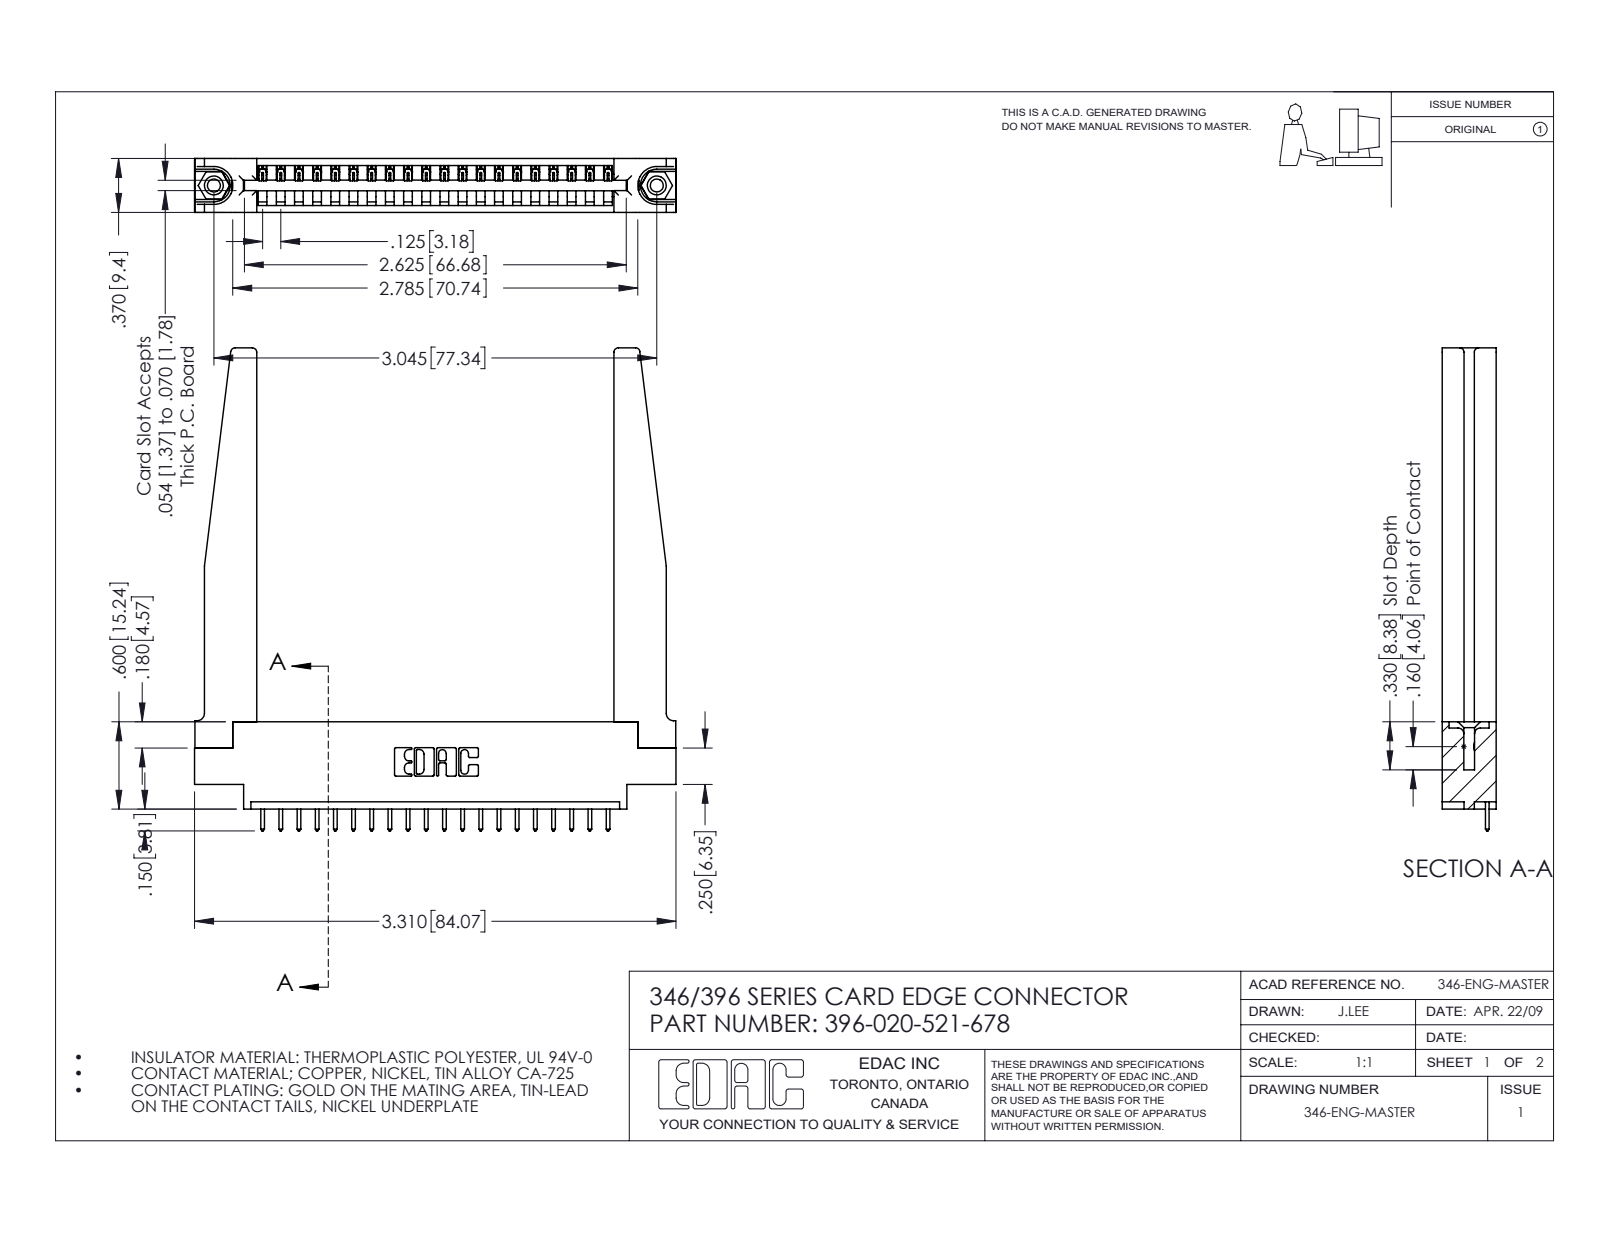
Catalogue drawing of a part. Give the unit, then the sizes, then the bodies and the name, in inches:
Units: inches
Overall size (bounding box): 3.32 × 3.31 × 0.37
Round holes (diameter × count): ⌀0.089 ×2, ⌀0.125 ×2, ⌀0.156 ×2, ⌀0.064 ×1
Round bosses / shafts (diameter × count): ⌀0.155 ×2
Partial cylindrical surfaces — rounded edges, fillets, slot ends (radius × count): R0.006 ×40, R0.01 ×40, R0.01 ×22, R0.03 ×8, R0.007 ×6, R0.031 ×6, R0.026 ×3, R0.031 ×2
Main face-to-face distances: 0.37, 0.072, 0.048, 0.322, 0.15, 0.148, 0.25, 0.298, 0.025, 0.102
Hole centre spacings: 0.246, 2.837, 3.045
Volume: 0.891 in³ · Surface area: 24.55 in²
Bodies: 25 solids, 1520 faces (1022 planar, 446 cylindrical, 52 other)
Part name (STEP PRODUCT): 345-292-001_345-293-121; 346 Part_0.170 Offset - 0.156 Dia-TH; 345-250-001_345-250-001-102; 346-220-078_345-220-078 (+1 more)
STEP written by: SolidWorks 2016 (CONFIG_CONTROL_DESIGN)
